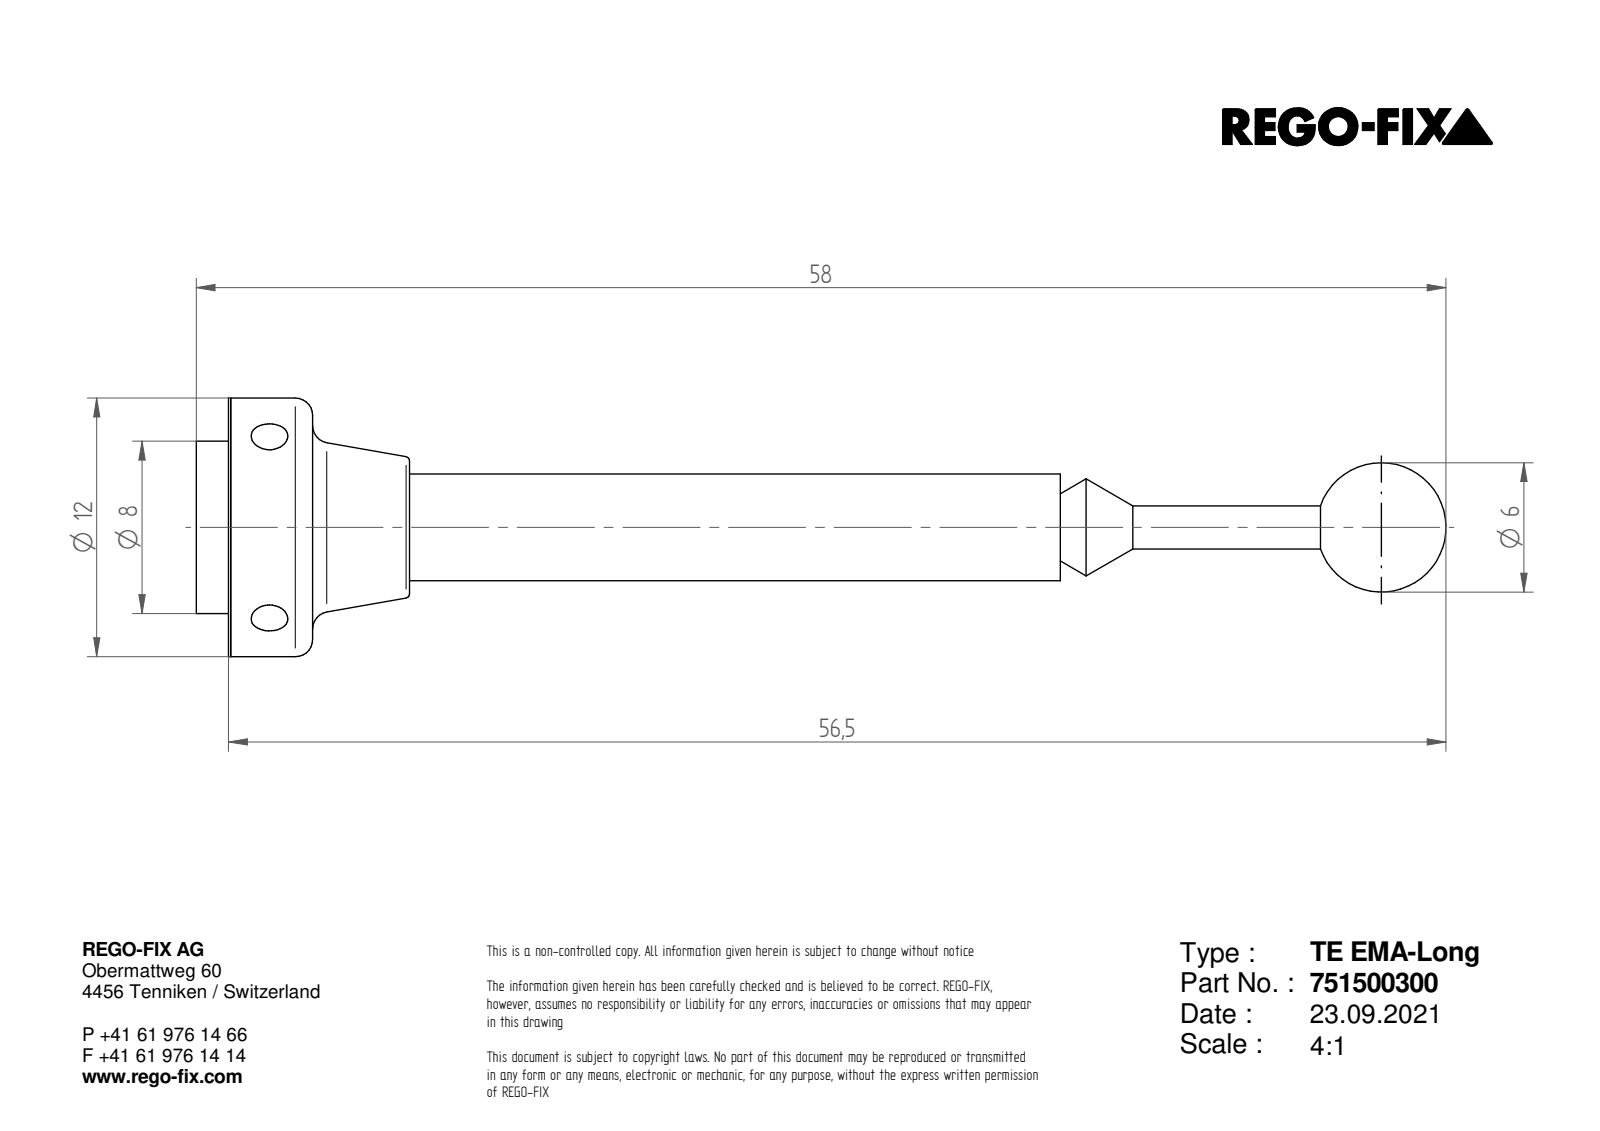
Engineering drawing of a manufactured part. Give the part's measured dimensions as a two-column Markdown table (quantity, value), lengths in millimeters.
| quantity | value |
| --- | --- |
| part name | 0025252 |
| STEP written by | ST-DEVELOPER v16.7 (AUTOMOTIVE_DESIGN) |
| units | millimeters |
| bodies | 2 solids, 28 faces (7 planar, 9 cylindrical, 12 other) |
| overall size | 58 × 12 × 12 |
| volume | 927 mm³ |
| surface area | 1 398 mm² |
| round holes (diameter × count) | 1.7 × 2 |
| round bosses / shafts (diameter × count) | 12 × 1, 8 × 1, 4.95 × 1, 2 × 1 |
| main face-to-face distances | 1.6, 1.5, 3.8, 3.9, 5.4, 34.7, 38.5, 38.6, 40.1, 30.2 |
